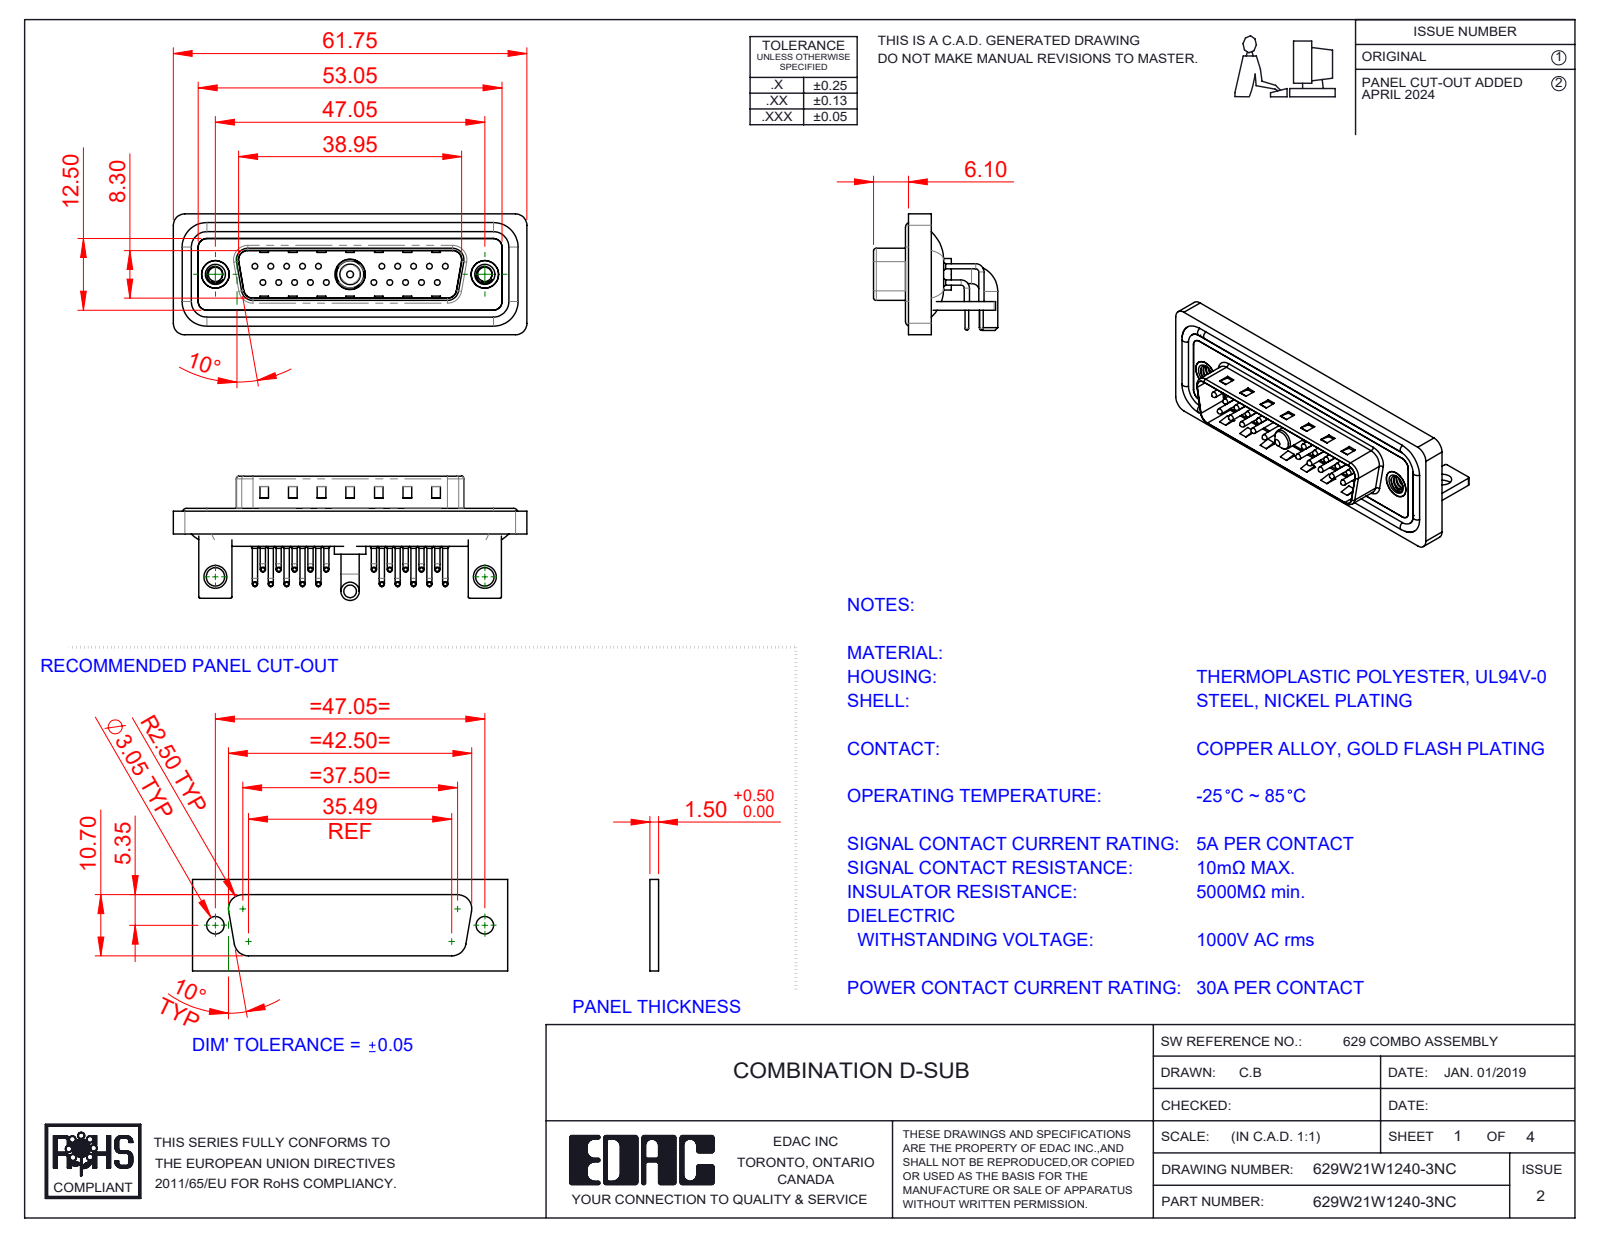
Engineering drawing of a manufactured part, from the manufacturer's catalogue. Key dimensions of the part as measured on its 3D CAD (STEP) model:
Part name (STEP PRODUCT): Power Pin_30A RA; 629Combo Contact Row 2; 629Combo Threaded Rivet_B; 629W21W1240-3NC (+6 more)
STEP written by: SolidWorks 2023 (CONFIG_CONTROL_DESIGN)
Units: millimetres
Bodies: 31 solids, 2764 faces (1519 planar, 947 cylindrical, 298 other)
Overall size (bounding box): 61.75 × 21.7 × 21.1
Volume: 7 718 mm³ · Surface area: 13 327 mm²
Round holes (diameter × count): ⌀0.75 ×20, ⌀1.6 ×20, ⌀2 ×20, ⌀2.5 ×2, ⌀3.2 ×2, ⌀4 ×2, ⌀4.8 ×2, ⌀5 ×2, ⌀4.85 ×1, ⌀5.3 ×1
Round bosses / shafts (diameter × count): ⌀0.9 ×40, ⌀1.5 ×20, ⌀1 ×20, ⌀0.65 ×20, ⌀1.6 ×4, ⌀4.9 ×2, ⌀3.2 ×2, ⌀5.5 ×1
Partial cylindrical surfaces — rounded edges, fillets, slot ends (radius × count): R1.01 ×20, R2 ×19, R1.5 ×18, R0.25 ×16, R0.5 ×9, R1.6 ×8, R0.6 ×4, R0.65 ×4
Main face-to-face distances: 0.4, 0.8, 2.1, 2.9, 1.5, 1.1, 4.1, 1.6, 4.5, 3.7
Hole centre spacings: 3.16, 2.77, 5.54, 8.31, 5.04, 19.39, 20.97, 22.16
